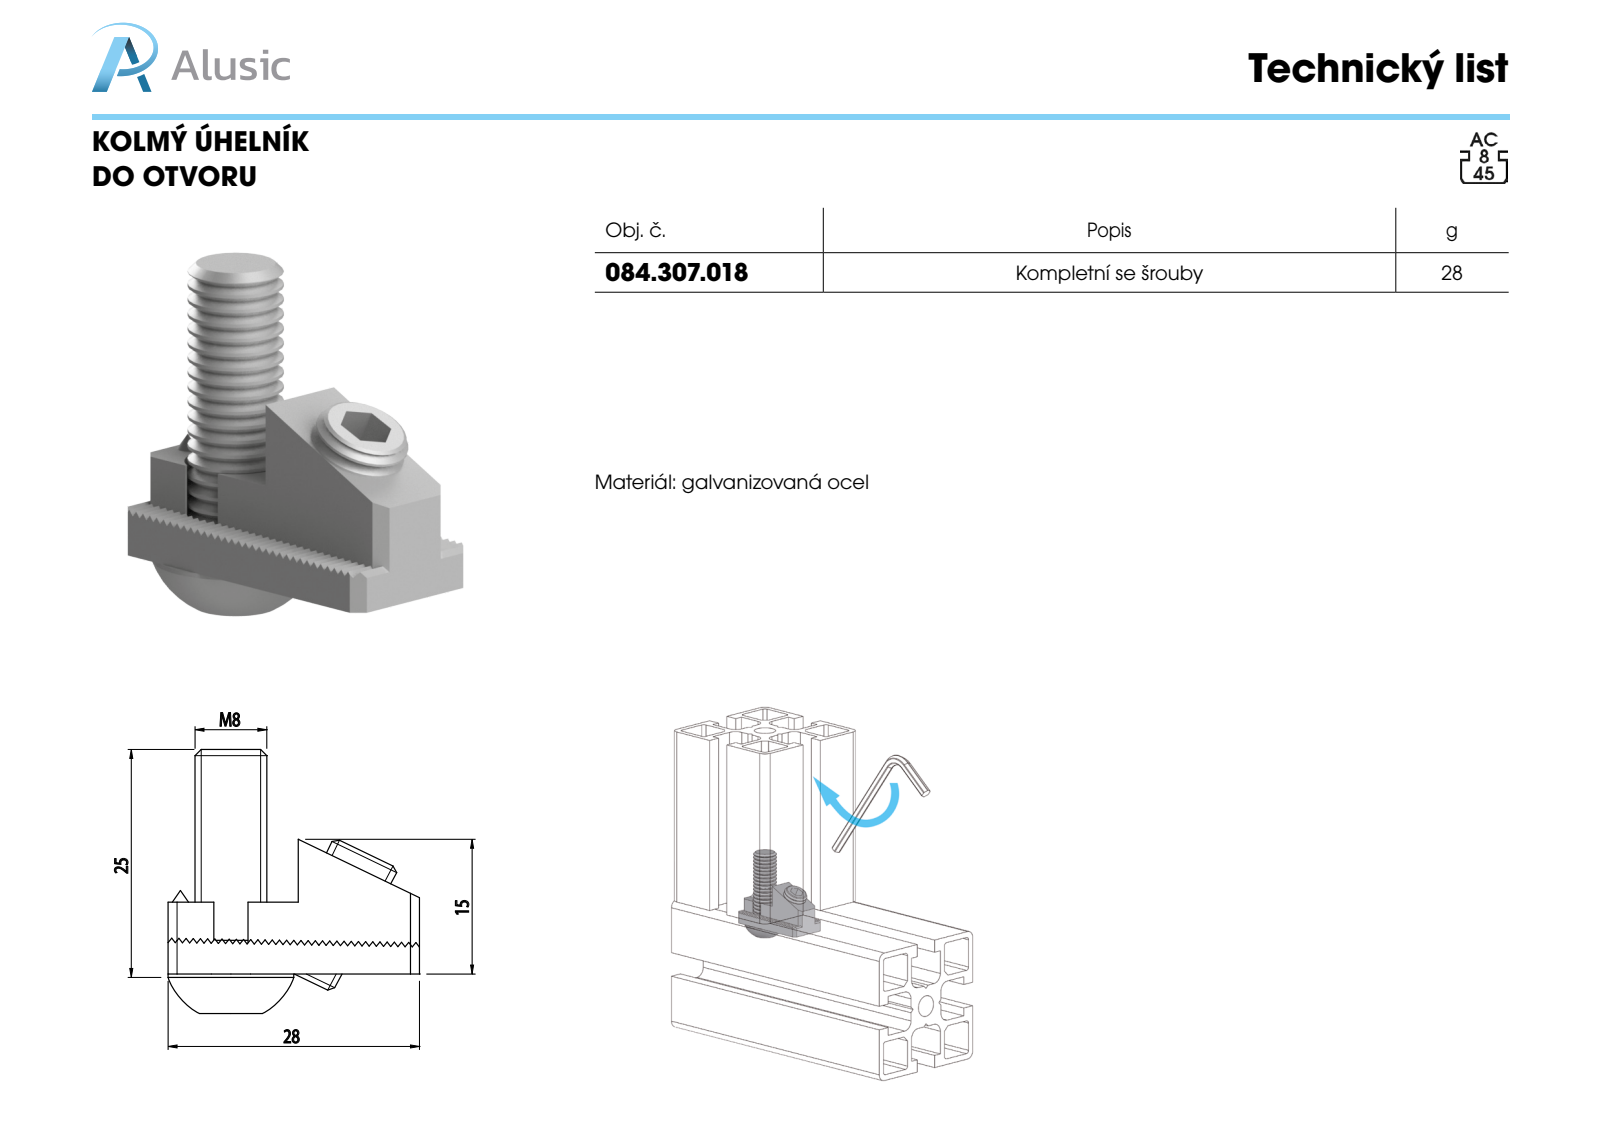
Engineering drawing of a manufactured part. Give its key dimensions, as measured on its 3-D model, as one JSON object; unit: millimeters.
{"part_name": "GRANI A PUNTA PIATTA UNI 5923_M8x16 UNI 5923; 084.307.018A; 084.307.018-L; 084.307.018", "step_written_by": "SolidWorks 2018 (AUTOMOTIVE_DESIGN)", "units": "millimeters", "bodies": {"solids": 3, "faces": 196, "planar": 55, "cylindrical": 53, "other": 88}, "overall_size": [29.5, 28, 13.3], "volume_mm3": 4084, "surface_area_mm2": 3514, "round_holes": [[6.8, 1], [8.5, 1]], "round_bosses_or_shafts": [[8, 2], [13, 1]], "face_to_face_distances": [8, 2.65, 10.65, 13.3, 28, 14.5, 13.5, 7.75, 25, 24.75]}
